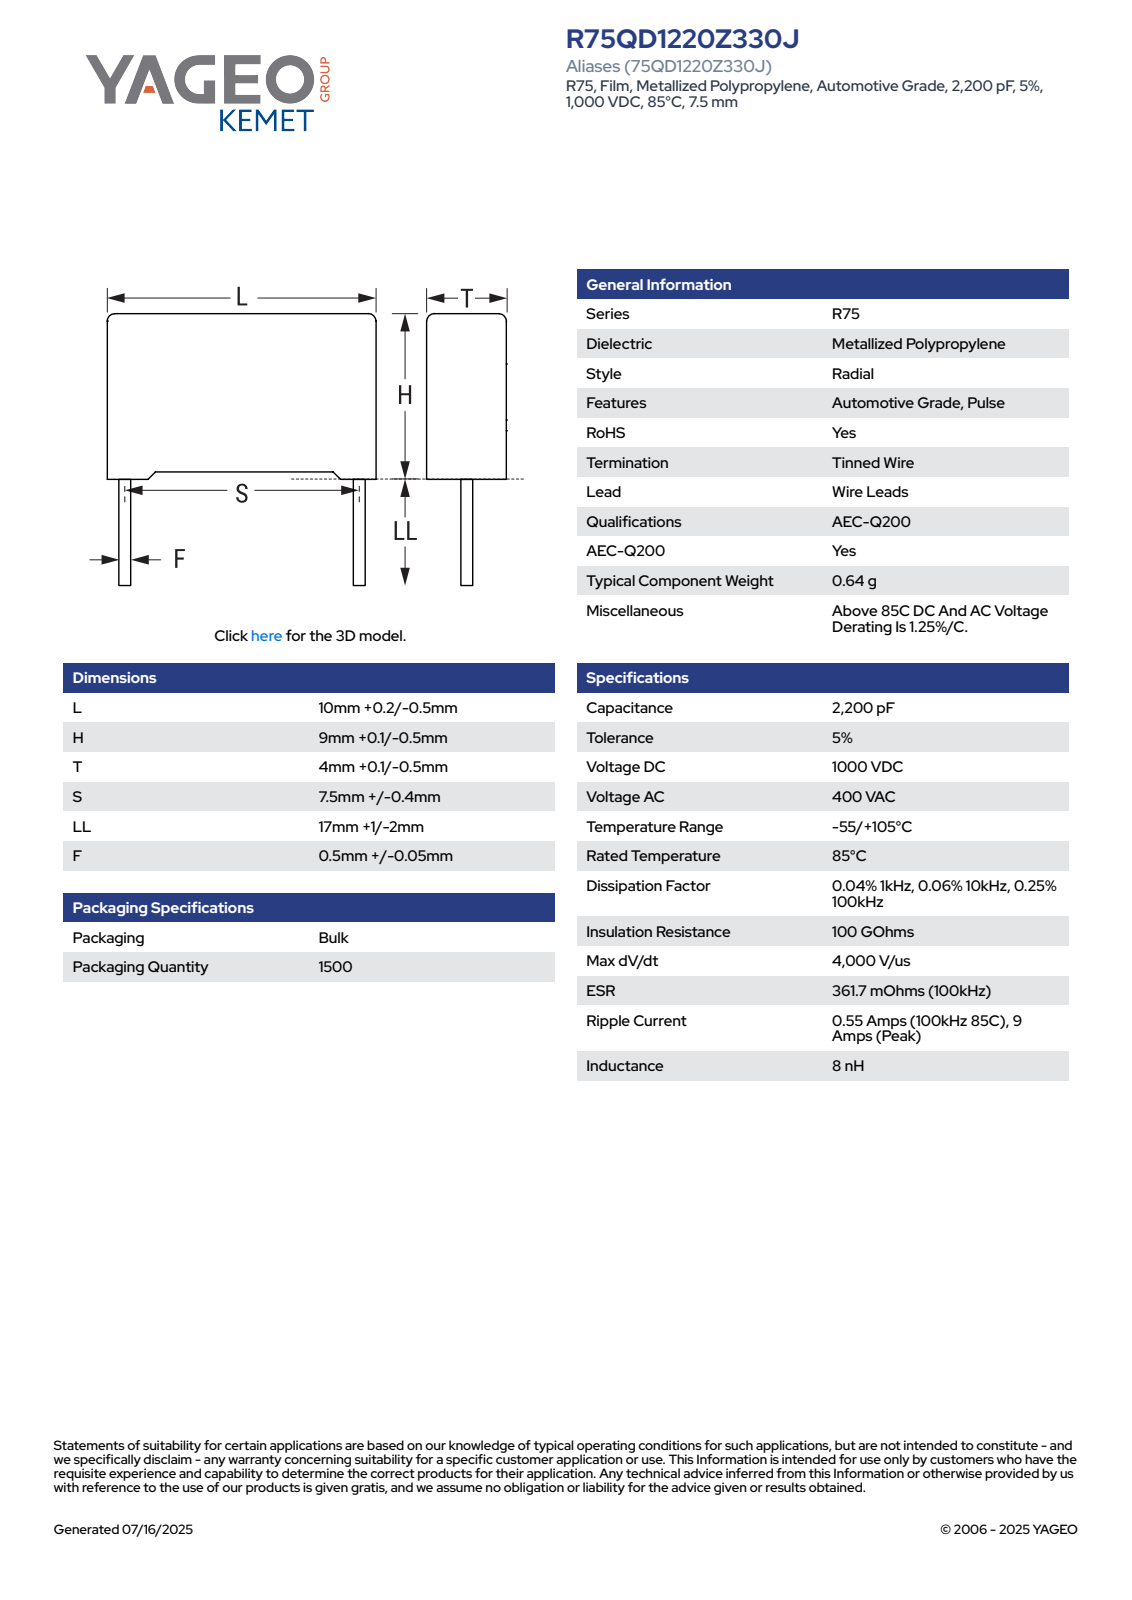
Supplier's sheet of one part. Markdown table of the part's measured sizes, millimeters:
| quantity | value |
| --- | --- |
| part name | CFR_RB2_10X9X4_L10.2H9.1T4.1S7.5LL18F0.55 |
| STEP written by | SolidWorks 2021 (AUTOMOTIVE_DESIGN) |
| units | millimeters |
| bodies | 4 solids, 85 faces (77 planar, 8 cylindrical, 0 other) |
| overall size | 27.1 × 10.2 × 4.11 |
| volume | 363 mm³ |
| surface area | 425 mm² |
| round bosses / shafts (diameter × count) | 0.55 × 2 |
| partial cylindrical surfaces (radius × count) | 0.5 × 4 |
| main face-to-face distances | 4.1, 10.2, 8.35, 0.34, 3.76, 0.75, 9.1, 3.42, 9.86, 0.31 |
